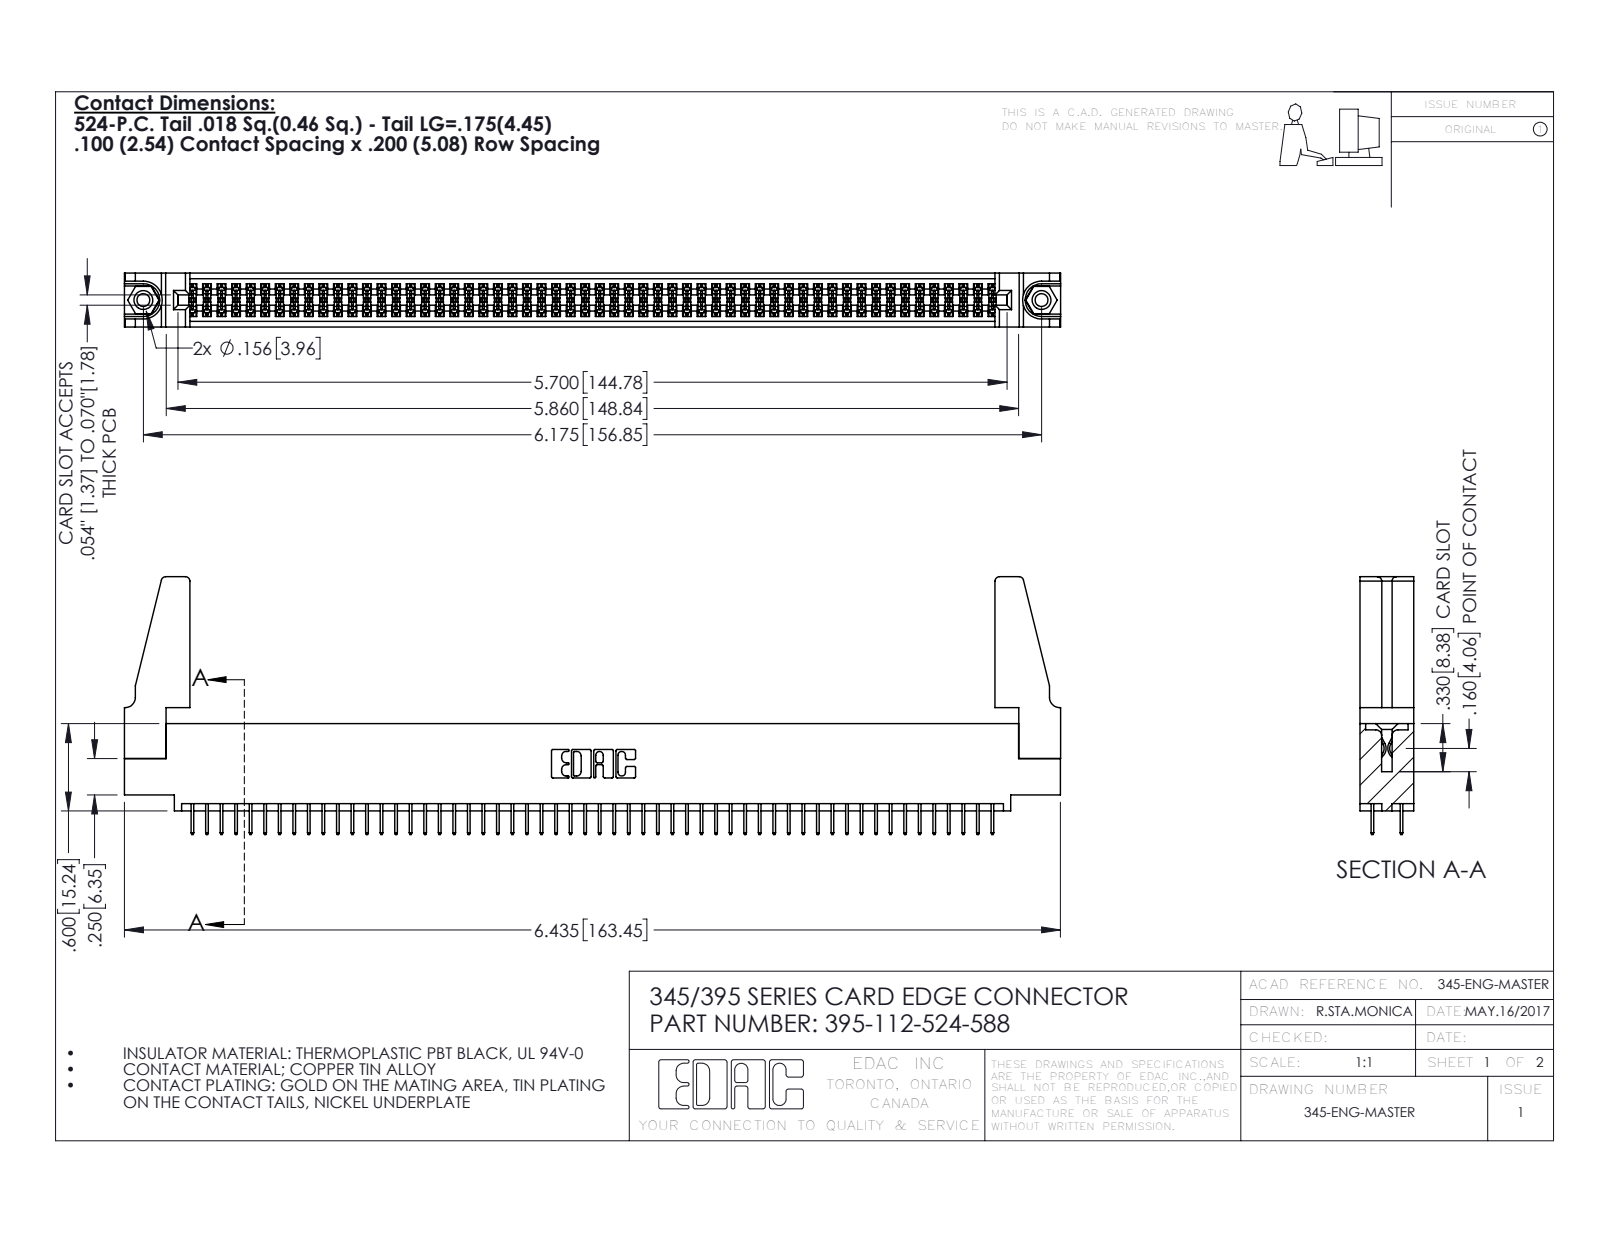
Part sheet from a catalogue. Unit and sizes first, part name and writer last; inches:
Units: inches
Overall size (bounding box): 6.436 × 1.772 × 0.37
Round holes (diameter × count): ⌀0.089 ×2, ⌀0.125 ×2, ⌀0.156 ×2, ⌀0.064 ×1
Round bosses / shafts (diameter × count): ⌀0.155 ×2
Partial cylindrical surfaces — rounded edges, fillets, slot ends (radius × count): R0.006 ×168, R0.01 ×22, R0.03 ×8, R0.007 ×6, R0.031 ×6, R0.026 ×3, R0.014 ×2, R0.019 ×2
Main face-to-face distances: 0.072, 0.298, 0.37, 0.2, 0.098, 0.272, 0.025, 0.225, 0.072, 0.175
Hole centre spacings: 0.27, 5.939, 6.175
Volume: 1.161 in³ · Surface area: 40.84 in²
Bodies: 117 solids, 6302 faces (4524 planar, 1762 cylindrical, 16 other)
Part name (STEP PRODUCT): 345 Part_0.110 Offset - 0.156 Dia-TH; 345-292-001_345-293-124; 345-220-078_345-220-088; 395-112-524-588 (+1 more)
STEP written by: SolidWorks 2016 (CONFIG_CONTROL_DESIGN)
